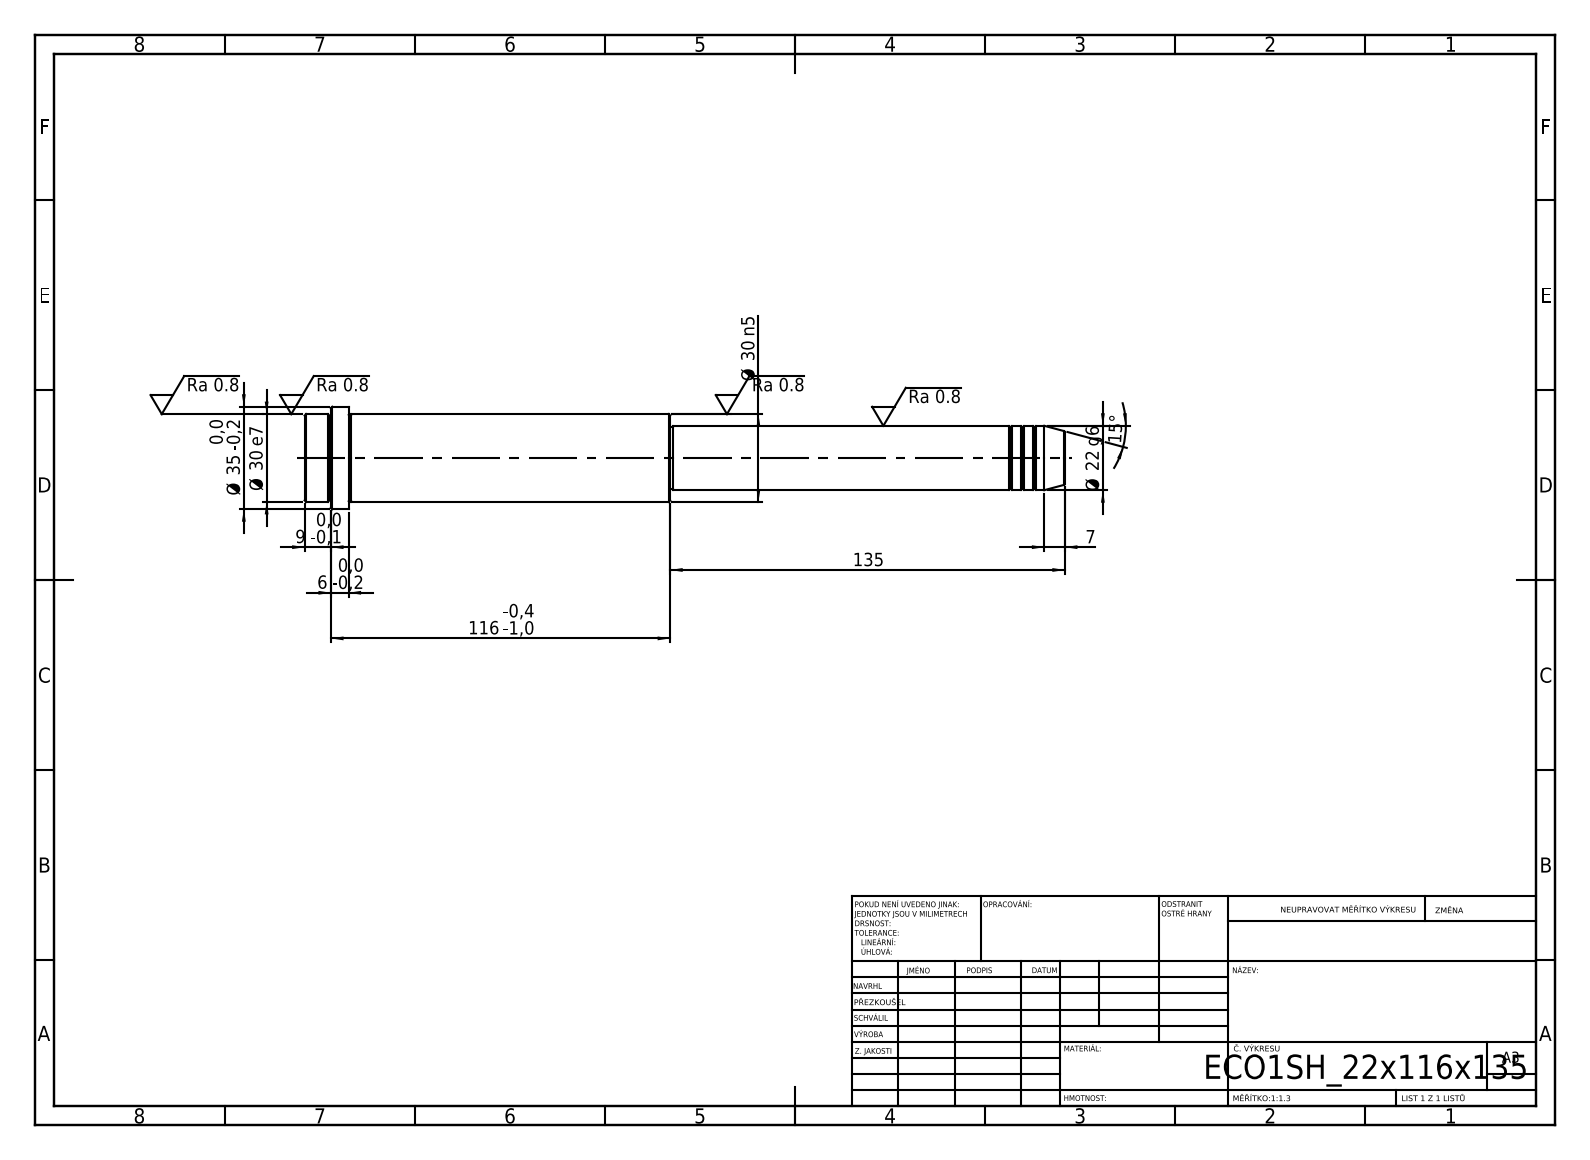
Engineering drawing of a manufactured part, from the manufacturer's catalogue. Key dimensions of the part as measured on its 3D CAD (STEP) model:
STEP written by: SolidWorks 2019 (CONFIG_CONTROL_DESIGN)
Units: millimetres
Bodies: 1 solid, 52 faces (6 planar, 16 cylindrical, 30 other)
Overall size (bounding box): 260 × 35 × 35
Volume: 140 554 mm³ · Surface area: 23 165 mm²
Round bosses / shafts (diameter × count): ⌀35 ×1, ⌀30 ×1, ⌀22 ×1, ⌀21 ×1
Main face-to-face distances: 125, 110, 15, 135, 245, 260, 251, 116, 6, 9
